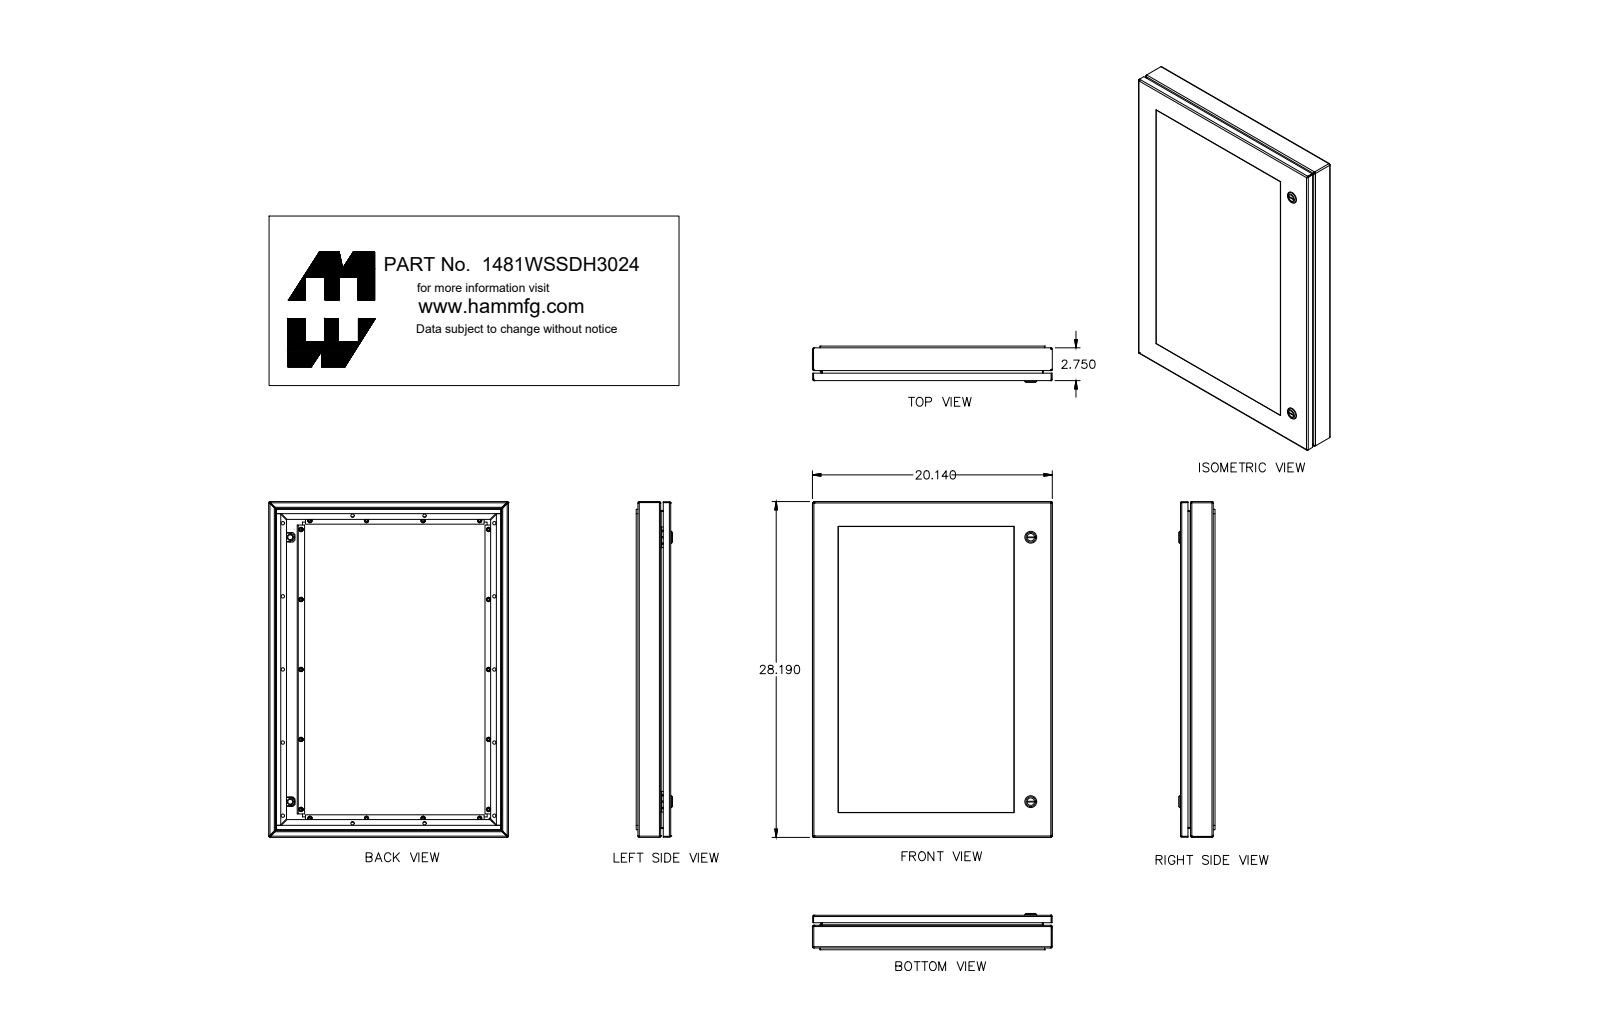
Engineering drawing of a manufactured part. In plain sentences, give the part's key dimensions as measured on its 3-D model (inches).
The part is named "1481WSSDH3024_Default". Its 3-D file was written by "SolidWorks 2019 (CONFIG_CONTROL_DESIGN)". It is 62 solids with 1387 faces: 754 planar, 406 cylindrical and 227 other. Overall it measures 28.19 by 20.14 by 2.91 inches. Its volume is 148.3 cubic inches and its surface area 2 403 square inches. Round holes: 17 of diameter 0.13, 14 of diameter 0.281, 2 of diameter 0.136, 2 of diameter 0.197, 2 of diameter 0.387, 2 of diameter 0.5, 2 of diameter 0.63, 2 of diameter 0.768, 1 of diameter 0.24, 1 of diameter 0.242. Round bosses or shafts: 18 of diameter 0.226, 18 of diameter 0.164, 17 of diameter 0.368, 2 of diameter 1.1, 2 of diameter 0.785, 2 of diameter 0.625, 2 of diameter 0.525, 2 of diameter 0.236. Partial cylindrical surfaces (rounded edges, fillets, slot ends): 36 of radius 0.101, 28 of radius 0.036, 28 of radius 0.108, 4 of radius 0.016, 4 of radius 0.088, 4 of radius 0.125, 2 of radius 0.307, 1 of radius 0.021. The main face-to-face distances are 0.072, 0.25, 0.178, 2.578, 2.328, 0.842, 1.736, 0.592, 20.068, 2.65. The hole center spacings are 6.137, 18.794, 4.75, 12.274, 21.592, 25.447, 17.764, 5.893.
